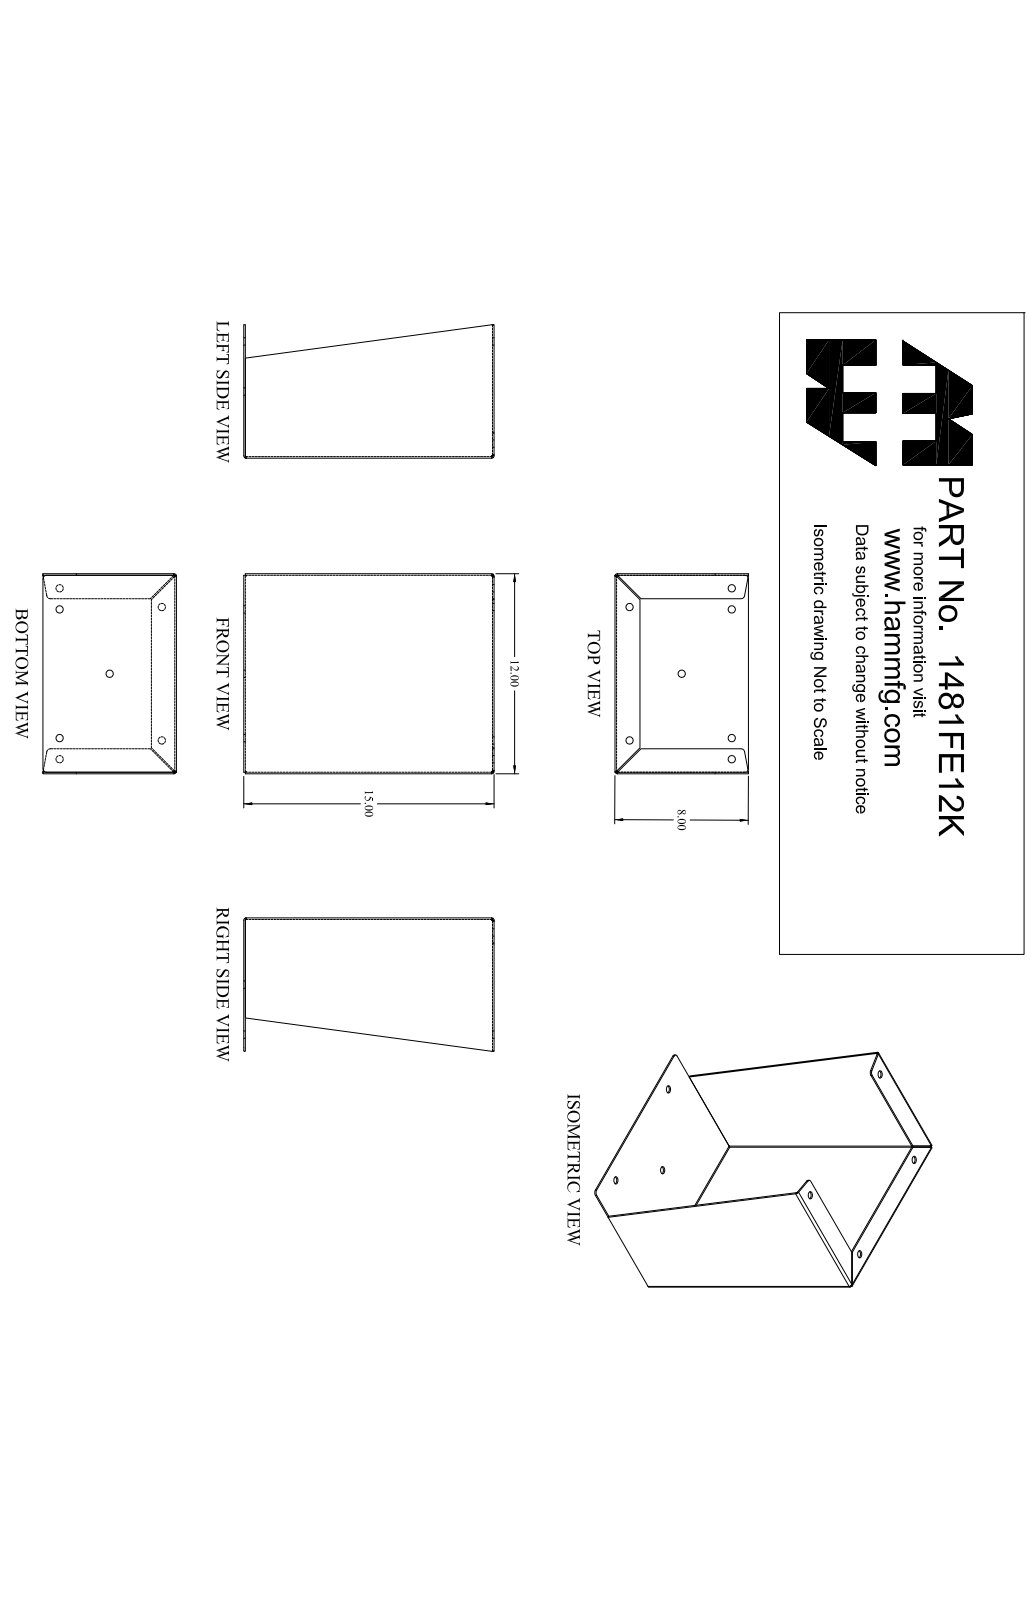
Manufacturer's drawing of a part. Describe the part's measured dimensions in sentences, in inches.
The part is named "1481FE12K_Default". Its 3-D file was written by "SolidWorks 2019 (CONFIG_CONTROL_DESIGN)". It is 1 solid with 78 faces: 42 planar, 30 cylindrical and 6 other. Overall it measures 15 by 12 by 8 inches. Its volume is 48.42 cubic inches and its surface area 1 030 square inches. Round holes: 7 of diameter 0.437. Partial cylindrical surfaces (rounded edges, fillets, slot ends): 6 of radius 0.048, 6 of radius 0.143, 4 of radius 0.22. The main face-to-face distances are 0.095, 11.905, 12, 11.81, 0.095, 14.81, 14.905, 14.905, 15, 1.405. The hole center spacings are 4.888, 5.076, 6.126, 6.227, 9.964, 1.266, 1.266, 5.939.
